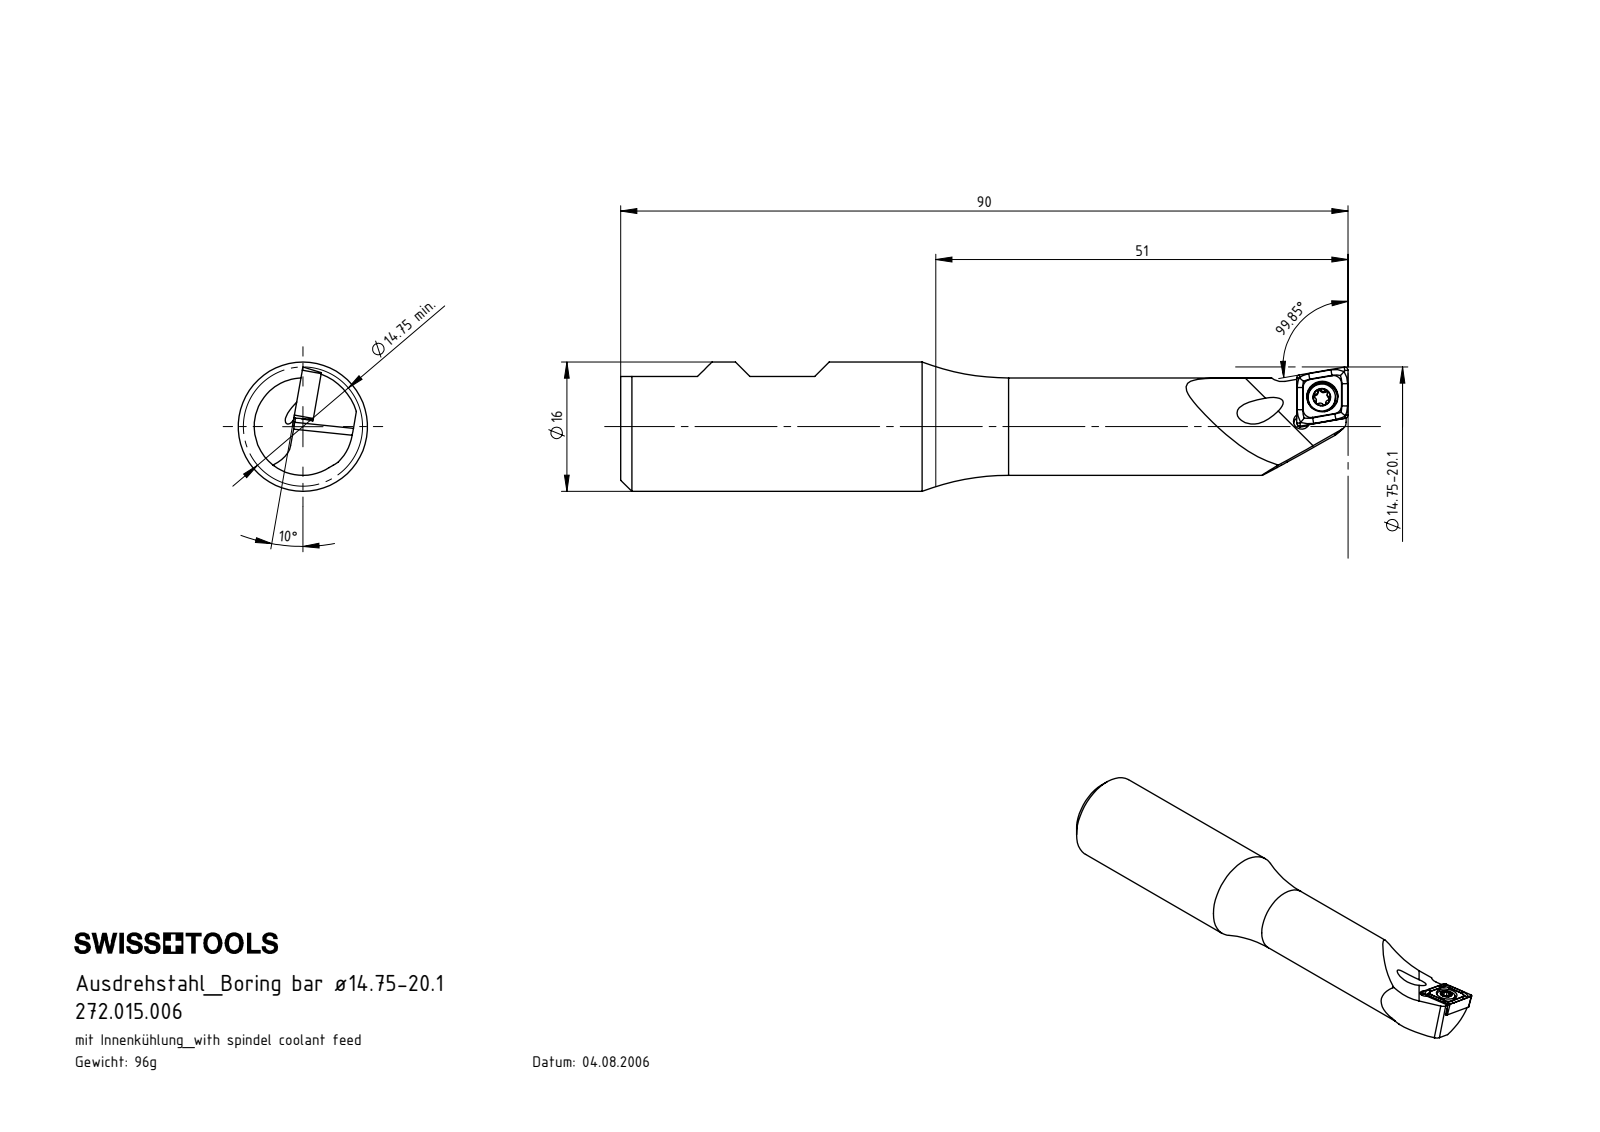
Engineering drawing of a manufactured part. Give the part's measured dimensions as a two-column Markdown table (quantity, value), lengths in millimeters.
| quantity | value |
| --- | --- |
| part name | B15.WCA.K11.090; WCA-ER2.001.006_A; CCMT060204; B15-WCA.K11.090_A |
| STEP written by | SolidWorks 2015 (AUTOMOTIVE_DESIGN) |
| units | millimeters |
| bodies | 3 solids, 126 faces (33 planar, 39 cylindrical, 54 other) |
| overall size | 90 × 16 × 16 |
| volume | 12 162 mm³ |
| surface area | 4 986 mm² |
| round holes (diameter × count) | 3 × 2, 2 × 1, 2.05 × 1, 2.8 × 1, 3.85 × 1 |
| round bosses / shafts (diameter × count) | 16 × 1, 12.05 × 1, 3.4 × 1, 2.5 × 1 |
| partial cylindrical surfaces (radius × count) | 0.21 × 6, 0.36 × 5, 0.36 × 1, 1 × 1, 6.2 × 1, 7 × 1, 8 × 1 |
| main face-to-face distances | 2.18, 10.25, 5.1, 7.28, 7.48, 2.38, 83.76, 1.48, 6.58, 0.7 |
| hole center spacings | 3.89, 3.99 |
